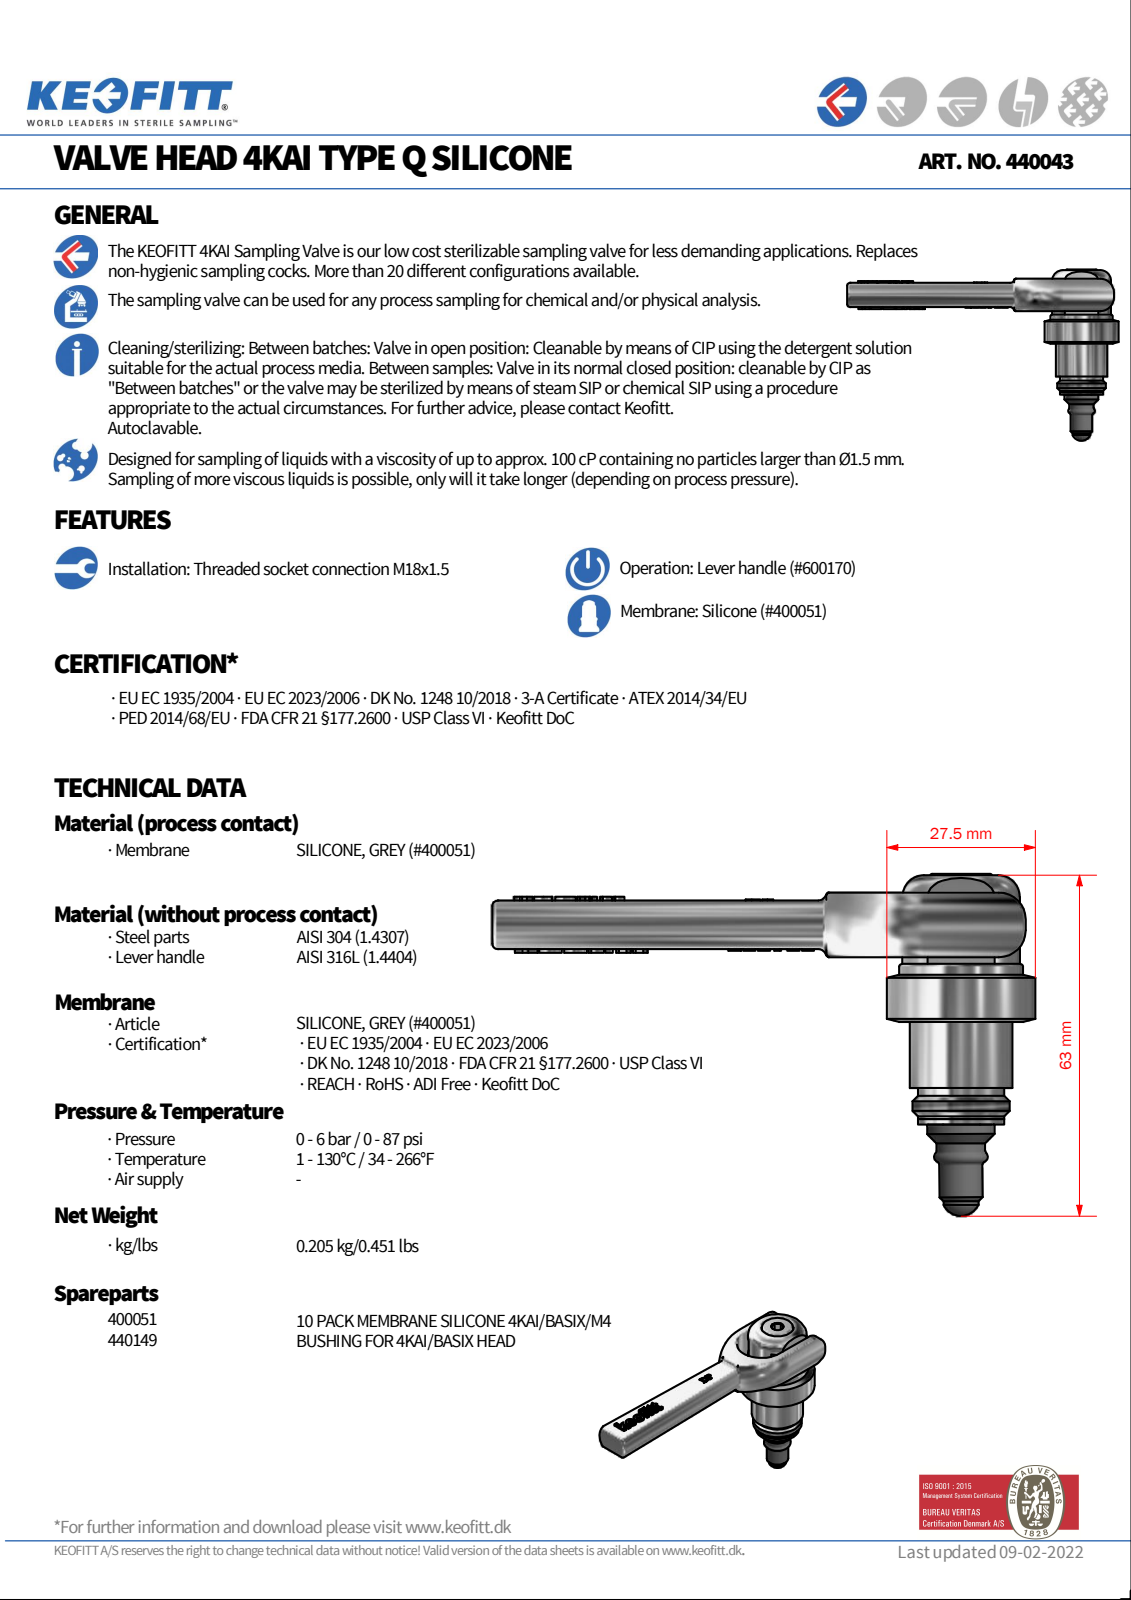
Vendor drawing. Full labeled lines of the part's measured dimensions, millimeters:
Part name (STEP PRODUCT): 440043E
STEP written by: Autodesk Inventor 2024 (AUTOMOTIVE_DESIGN)
Units: millimetres
Bodies: 2 solids, 536 faces (229 planar, 57 cylindrical, 250 other)
Overall size (bounding box): 100.75 × 68.5 × 27.5
Volume: 28 432 mm³ · Surface area: 10 660 mm²
Round bosses / shafts (diameter × count): ⌀27.5 ×1, ⌀25 ×1, ⌀19 ×1, ⌀18 ×1, ⌀16 ×1, ⌀12.5 ×1, ⌀10 ×1, ⌀9 ×1
Partial cylindrical surfaces — rounded edges, fillets, slot ends (radius × count): R0.5 ×14, R0.2 ×8, R1 ×2, R1.5 ×2, R3 ×2, R5 ×2, R9.1 ×1, R10.9 ×1
Main face-to-face distances: 1.5, 10.5, 3.5, 9, 12.5, 12, 3.3, 12.3, 14, 18.05
